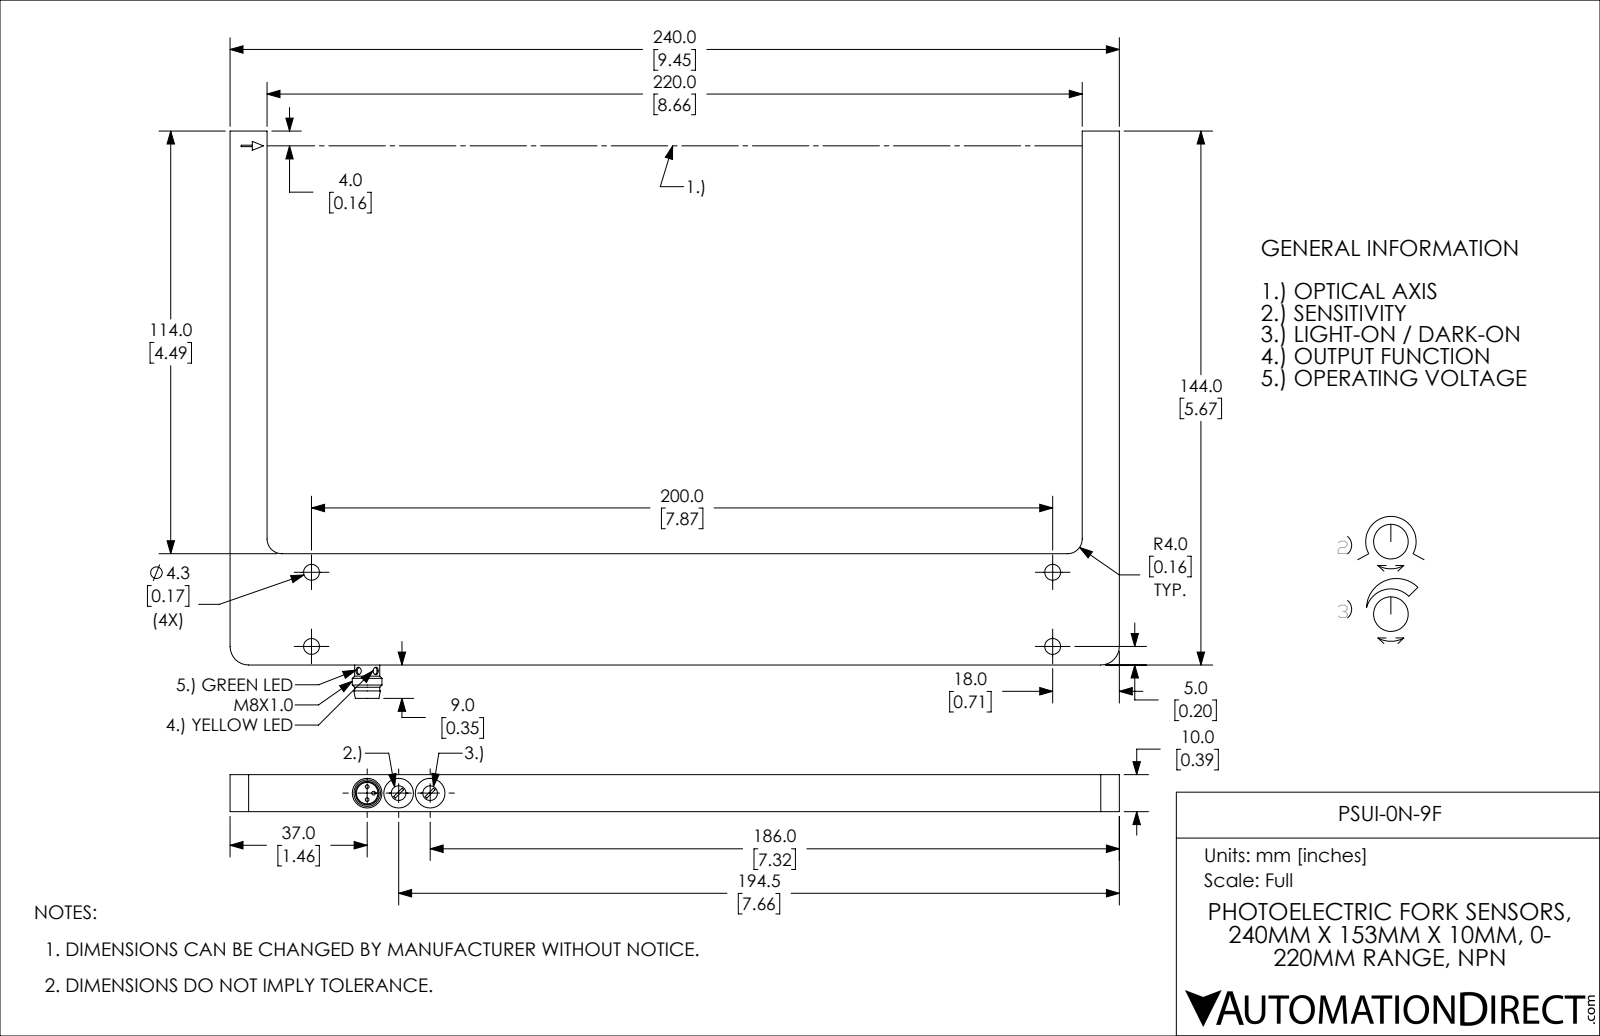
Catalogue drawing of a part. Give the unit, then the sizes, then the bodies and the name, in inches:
Units: inches
Overall size (bounding box): 9.449 × 6.024 × 0.394
Round holes (diameter × count): ⌀0.169 ×4, ⌀0.079 ×2, ⌀0.157 ×2, ⌀0.315 ×2, ⌀0.228 ×1
Round bosses / shafts (diameter × count): ⌀0.039 ×3, ⌀0.315 ×1, ⌀0.267 ×1
Partial cylindrical surfaces — rounded edges, fillets, slot ends (radius × count): R0.063 ×2, R0.157 ×2, R0.197 ×2
Main face-to-face distances: 0.394, 9.055, 1.181, 9.449, 8.661, 4.488, 5.669, 5.665, 1.177, 0.157
Hole centre spacings: 0.335, 0.787, 7.874, 7.913, 0.669
Volume: 5.76 in³ · Surface area: 45.93 in²
Bodies: 1 solid, 68 faces (35 planar, 27 cylindrical, 6 other)
Part name (STEP PRODUCT): PSUI-0N-9F
STEP written by: SolidWorks 2017 (AUTOMOTIVE_DESIGN)
